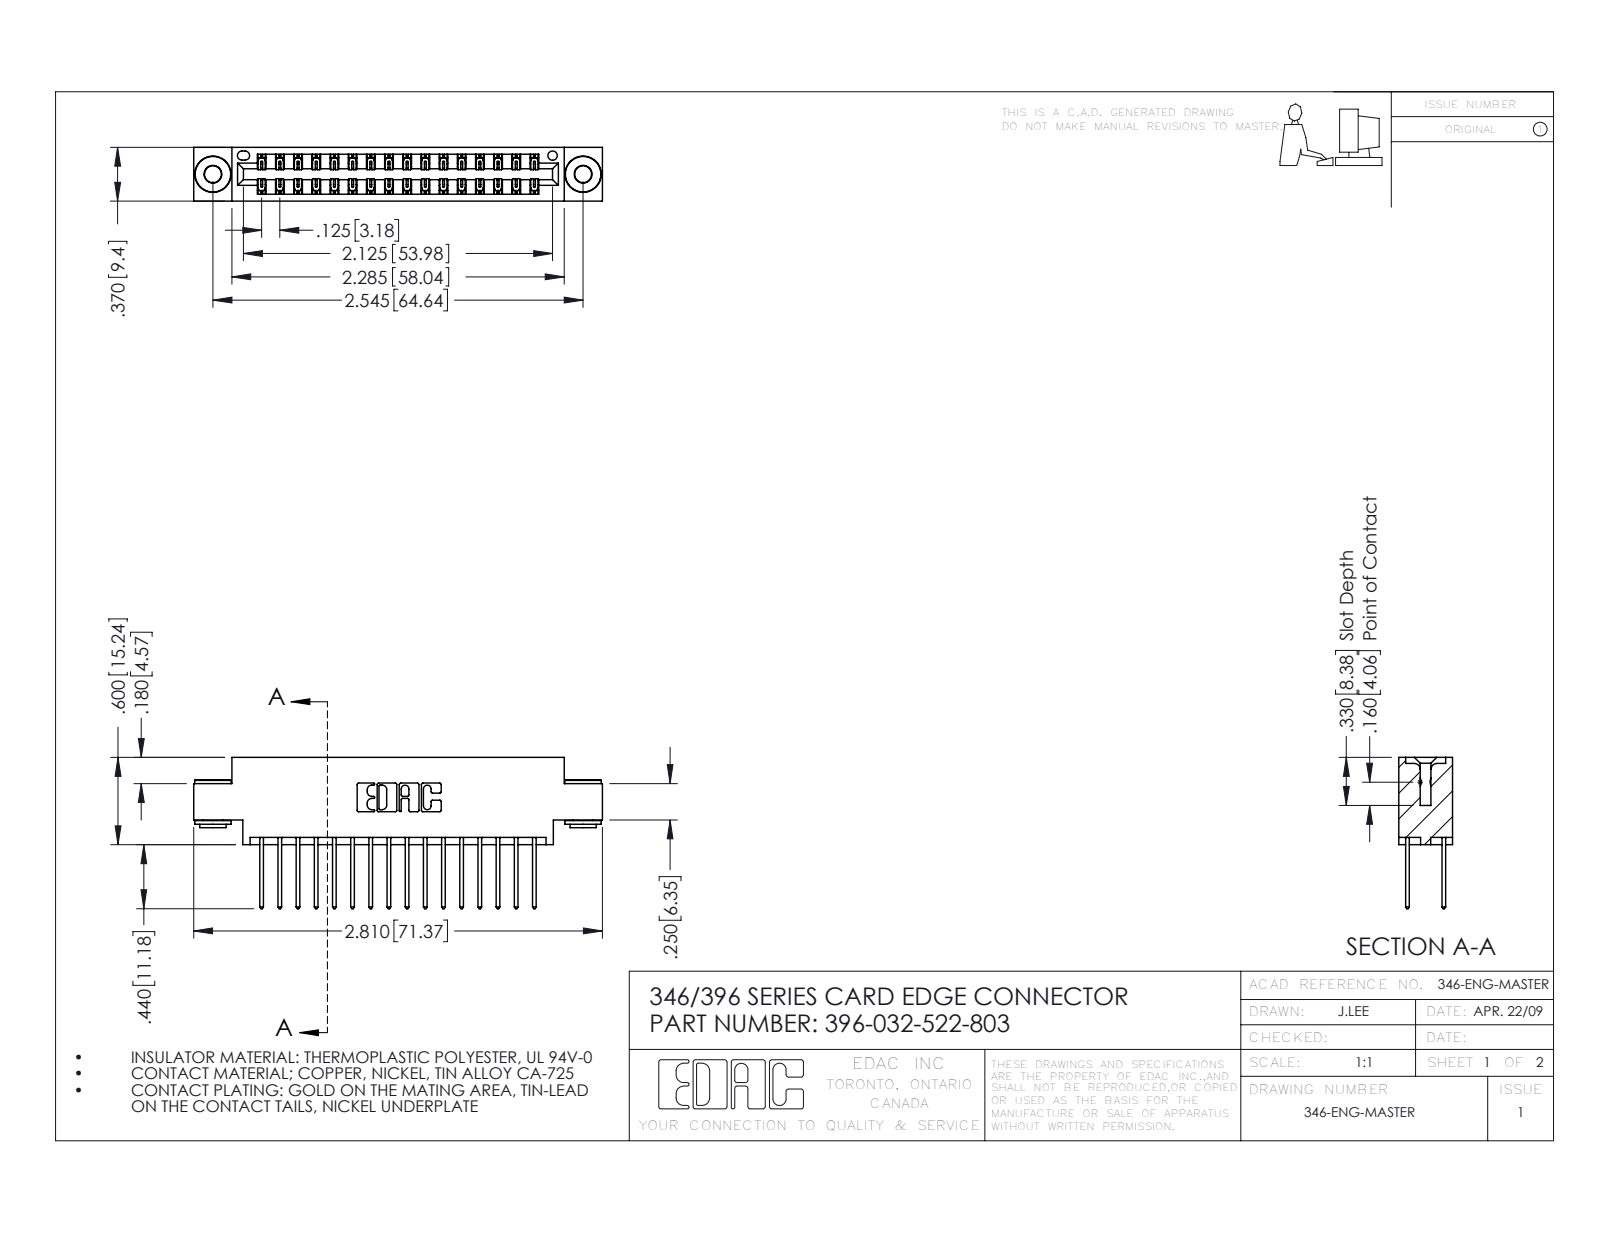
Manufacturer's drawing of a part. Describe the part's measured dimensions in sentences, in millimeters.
The part is named "346 Part_0.170 Offset - 0.156 Dia-TH; 396-032-522-803; 345-250-002_345-250-002-102; 345-292-001_345-293-122". Its 3-D file was written by "SolidWorks 2016 (CONFIG_CONTROL_DESIGN)". It is 35 solids with 1828 faces: 1210 planar, 610 cylindrical and 8 other. Overall it measures 71.4 by 26.4 by 9.4 millimeters. Its volume is 6 700 cubic millimeters and its surface area 9 581 square millimeters. Round holes: 2 of diameter 2.9, 2 of diameter 4, 1 of diameter 1.6. Round bosses or shafts: 2 of diameter 6.4, 2 of diameter 4.6, 2 of diameter 3.5. Partial cylindrical surfaces (rounded edges, fillets, slot ends): 48 of radius 0.2, 32 of radius 0.3, 22 of radius 0.3, 6 of radius 0.2, 6 of radius 0.8, 3 of radius 0.7, 2 of radius 0.4, 2 of radius 0.6. The main face-to-face distances are 1.2, 8.2, 6.4, 9.4, 0.6, 1.8, 7.6, 7, 3.8, 5.6. The hole center spacings are 6.2, 59.4, 64.6.
